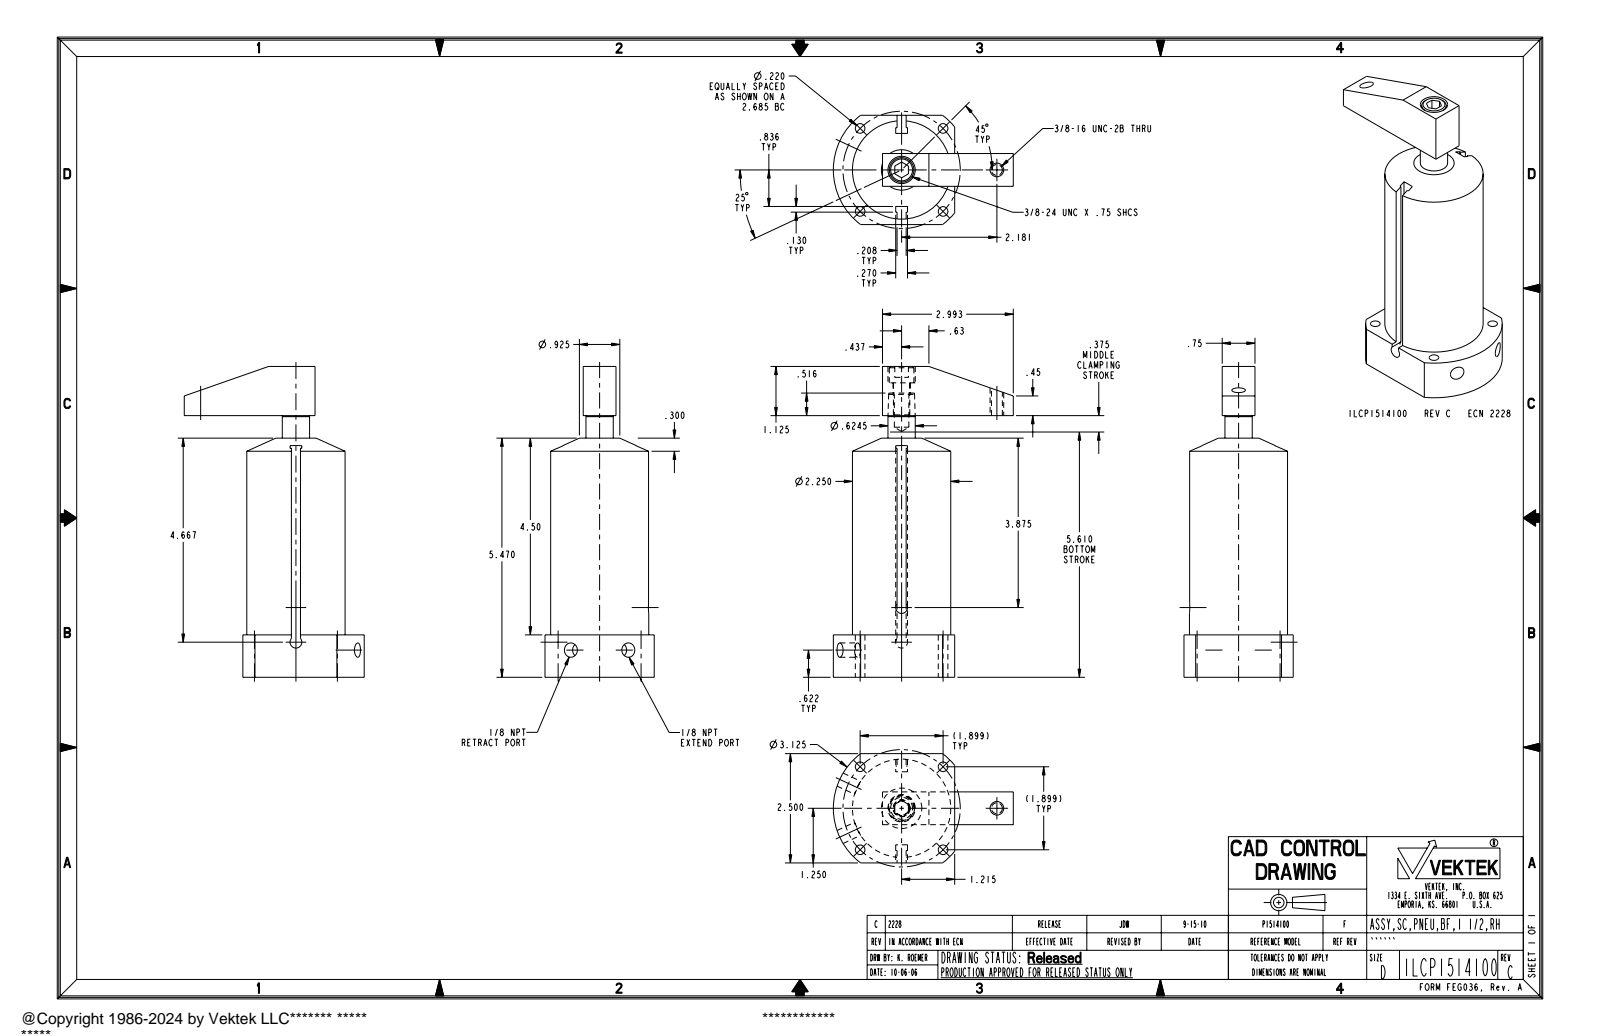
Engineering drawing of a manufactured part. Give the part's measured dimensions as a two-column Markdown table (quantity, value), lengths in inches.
| quantity | value |
| --- | --- |
| part name | ILCP1514100; ILC91501503; ILCP1514100_ASM |
| STEP written by | PRO/ENGINEER BY PARAMETRIC TECHNOLOGY CORPORATION, 2007460 (AUTOMOTIVE_DESIGN_CC2) |
| units | inches |
| bodies | 2 solids, 91 faces (43 planar, 36 cylindrical, 12 other) |
| overall size | 7.11 × 4.119 × 2.5 |
| volume | 24.77 in³ |
| surface area | 79.75 in² |
| round holes (diameter × count) | 0.22 × 4, 0.328 × 2, 0.312 × 1, 0.332 × 1, 0.39 × 1, 0.625 × 1 |
| round bosses / shafts (diameter × count) | 2.25 × 1, 0.624 × 1, 0.562 × 1, 0.375 × 1, 0.25 × 1 |
| partial cylindrical surfaces (radius × count) | 0.135 × 2, 1.563 × 1 |
| main face-to-face distances | 0.875, 1.625, 0.75, 0.415, 2.085, 0.461, 1.21, 0.97, 0.031, 0.239 |
| hole center spacings | 1.343, 1.898, 1.555, 2.685, 3.271, 2.181 |
